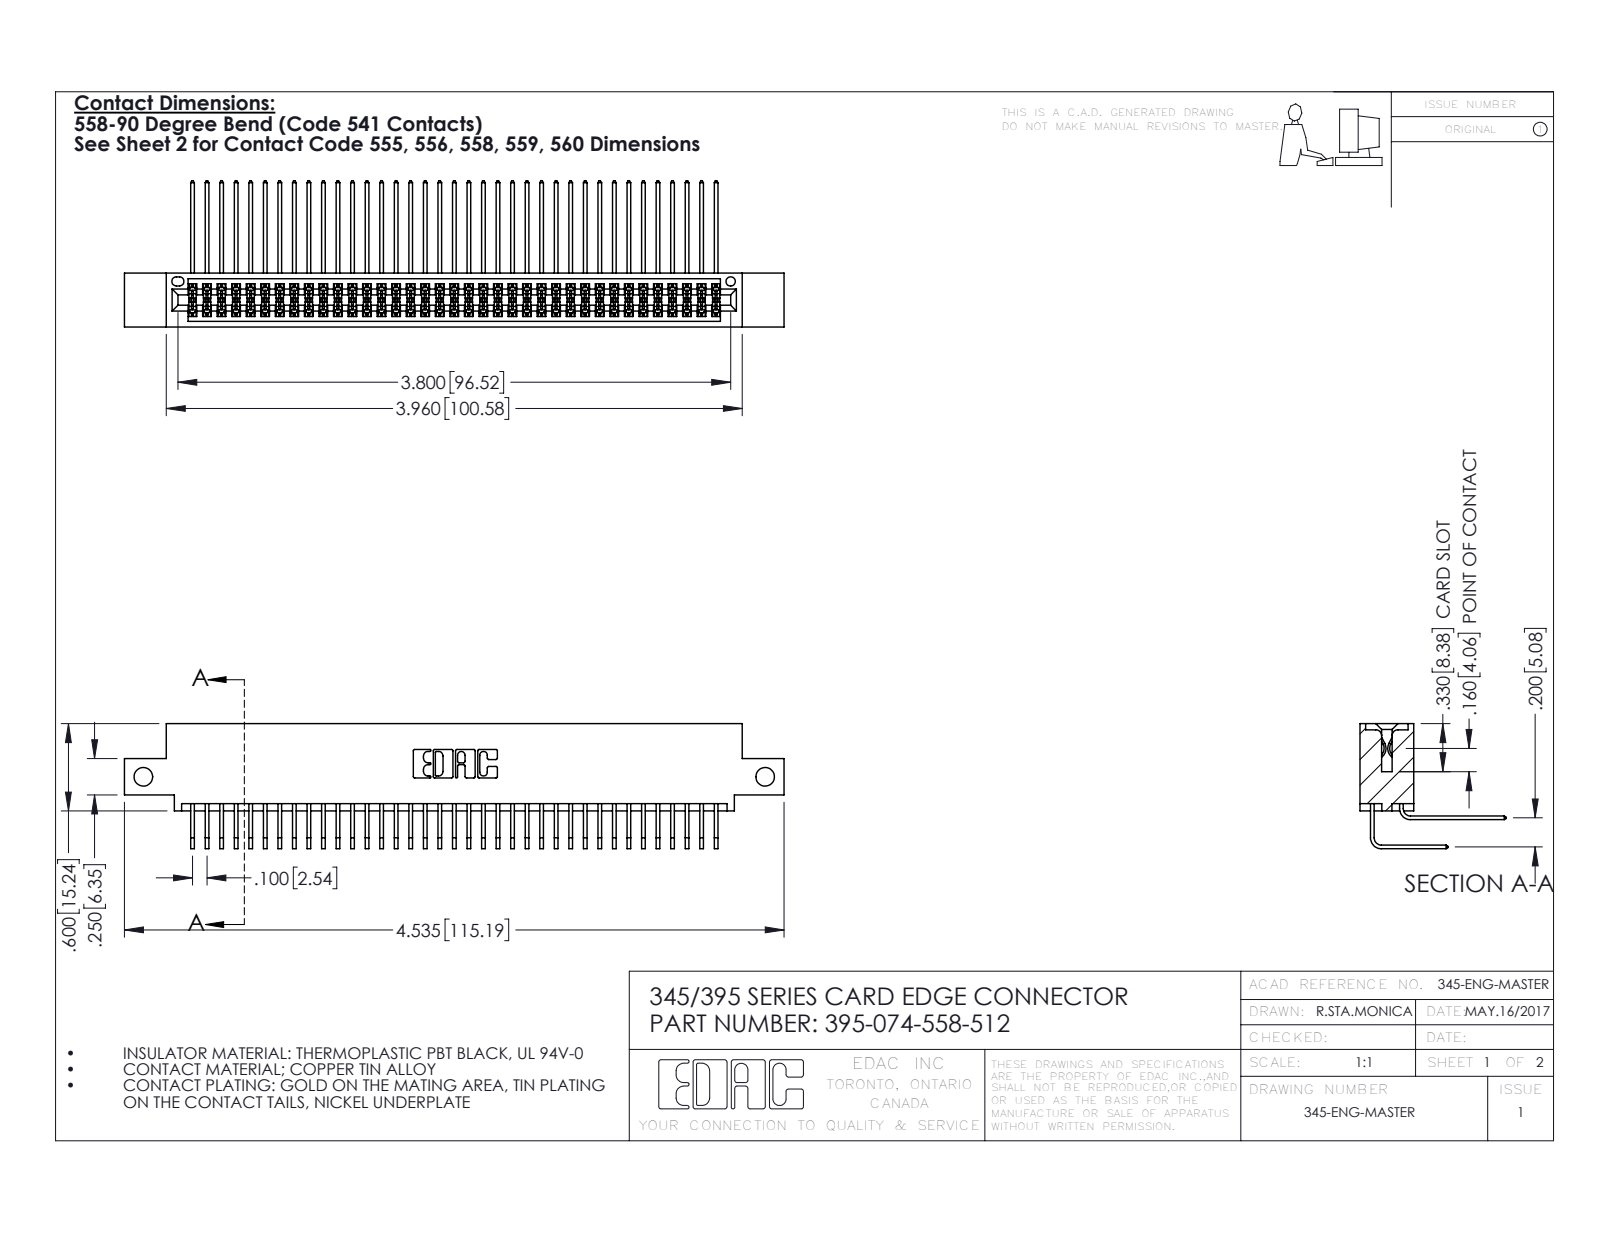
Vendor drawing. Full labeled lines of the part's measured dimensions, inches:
Part name (STEP PRODUCT): 345-292-001_558 Tail - 2; 345 Part_0.110 Offset - Side Mount; 345-292-001_558 559 Tail - 1; 395-074-558-512
STEP written by: SolidWorks 2016 (CONFIG_CONTROL_DESIGN)
Units: inches
Bodies: 75 solids, 3978 faces (2674 planar, 1304 cylindrical, 0 other)
Overall size (bounding box): 4.535 × 1.005 × 0.859
Volume: 0.696 in³ · Surface area: 29.04 in²
Round holes (diameter × count): ⌀0.128 ×2, ⌀0.064 ×1
Partial cylindrical surfaces — rounded edges, fillets, slot ends (radius × count): R0.006 ×112, R0.01 ×22, R0.007 ×6, R0.031 ×6, R0.026 ×3, R0.014 ×2, R0.019 ×2, R0.022 ×2
Main face-to-face distances: 0.072, 0.298, 0.2, 0.37, 0.098, 0.272, 0.025, 0.225, 0.025, 0.175
Hole centre spacings: 4.275
